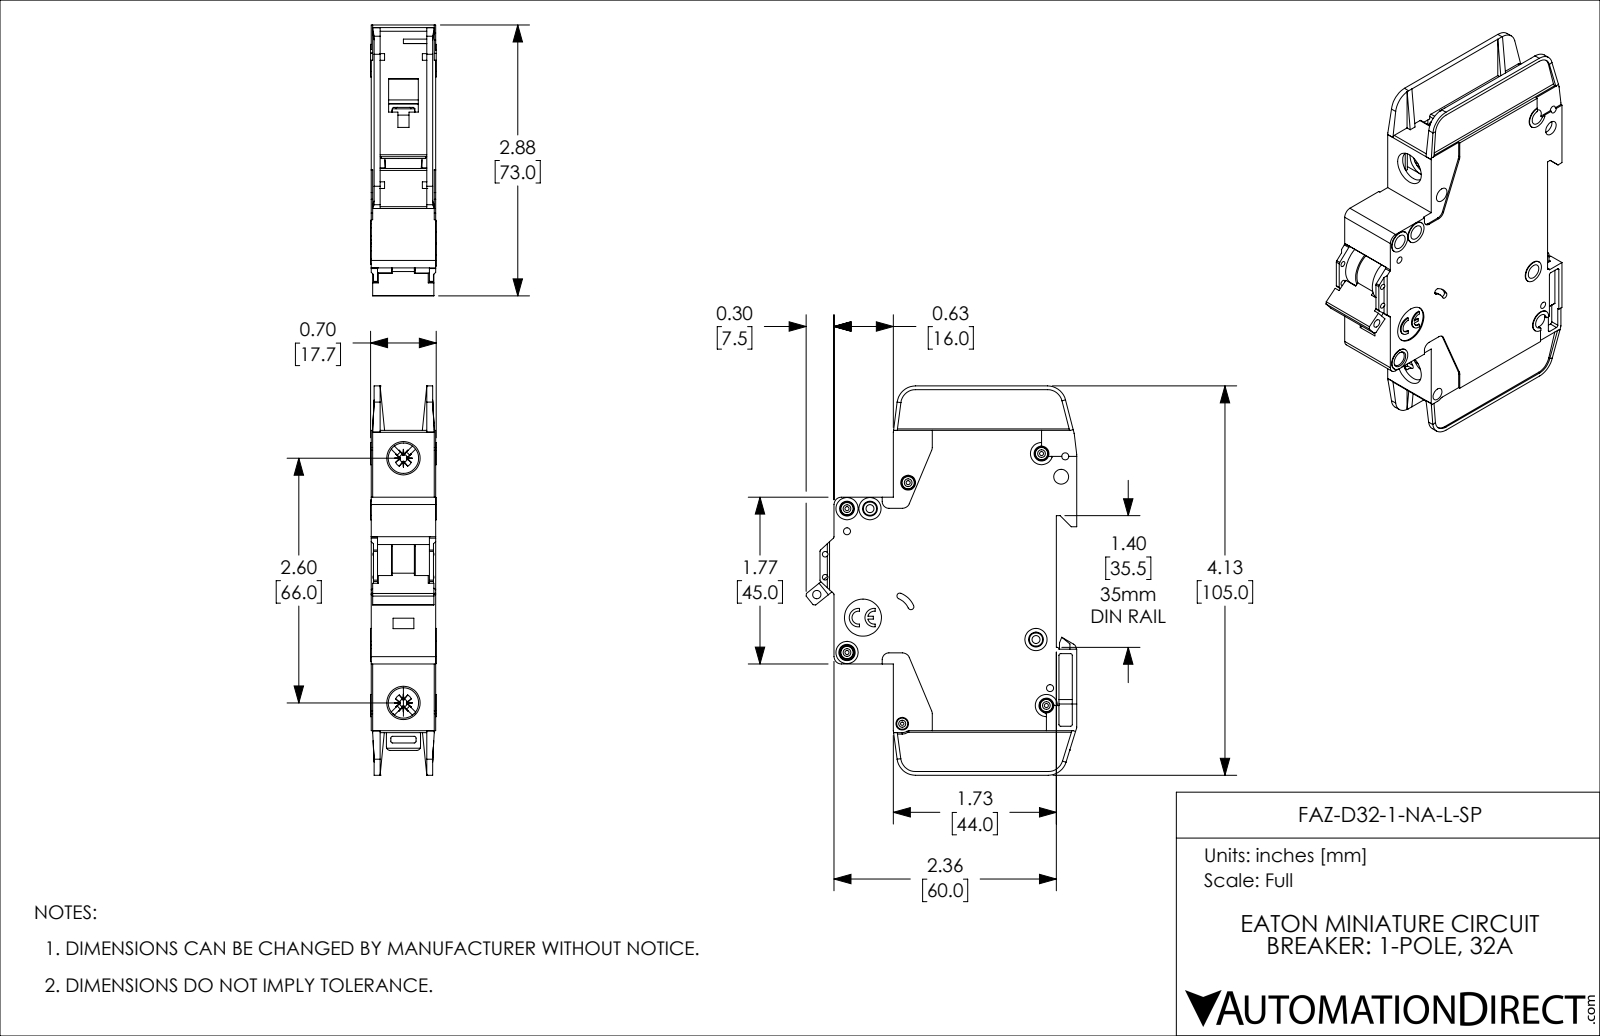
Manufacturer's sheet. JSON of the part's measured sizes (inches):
{"part_name": "FAZ-D32-1-NA-L-SP", "step_written_by": "SolidWorks 2019 (AUTOMOTIVE_DESIGN)", "units": "inches", "bodies": {"solids": 1, "faces": 1127, "planar": 671, "cylindrical": 357, "other": 99}, "overall_size": [4.134, 2.876, 0.697], "volume_in3": 4.682, "surface_area_in2": 41.01, "round_holes": [[0.157, 8], [0.043, 5], [0.075, 4], [0.059, 2], [0.085, 2], [0.323, 2], [0.035, 1], [0.089, 1], [0.098, 1], [0.134, 1], [0.394, 1]], "round_bosses_or_shafts": [[0.13, 5], [0.236, 4], [0.118, 2], [0.098, 1]], "partial_cylinders_radius": [[0.02, 42], [0.016, 10], [0.039, 10], [0.079, 8], [0.197, 5], [0.008, 4], [0.026, 4], [0.043, 4]], "face_to_face_distances": [0.047, 0.685, 0.591, 0.638, 0.094, 0.543, 0.016, 0.031, 0.496, 0.575], "hole_center_spacings": [0.244, 0.537, 0.87, 0.189, 0.199, 0.204, 0.221, 0.24]}
